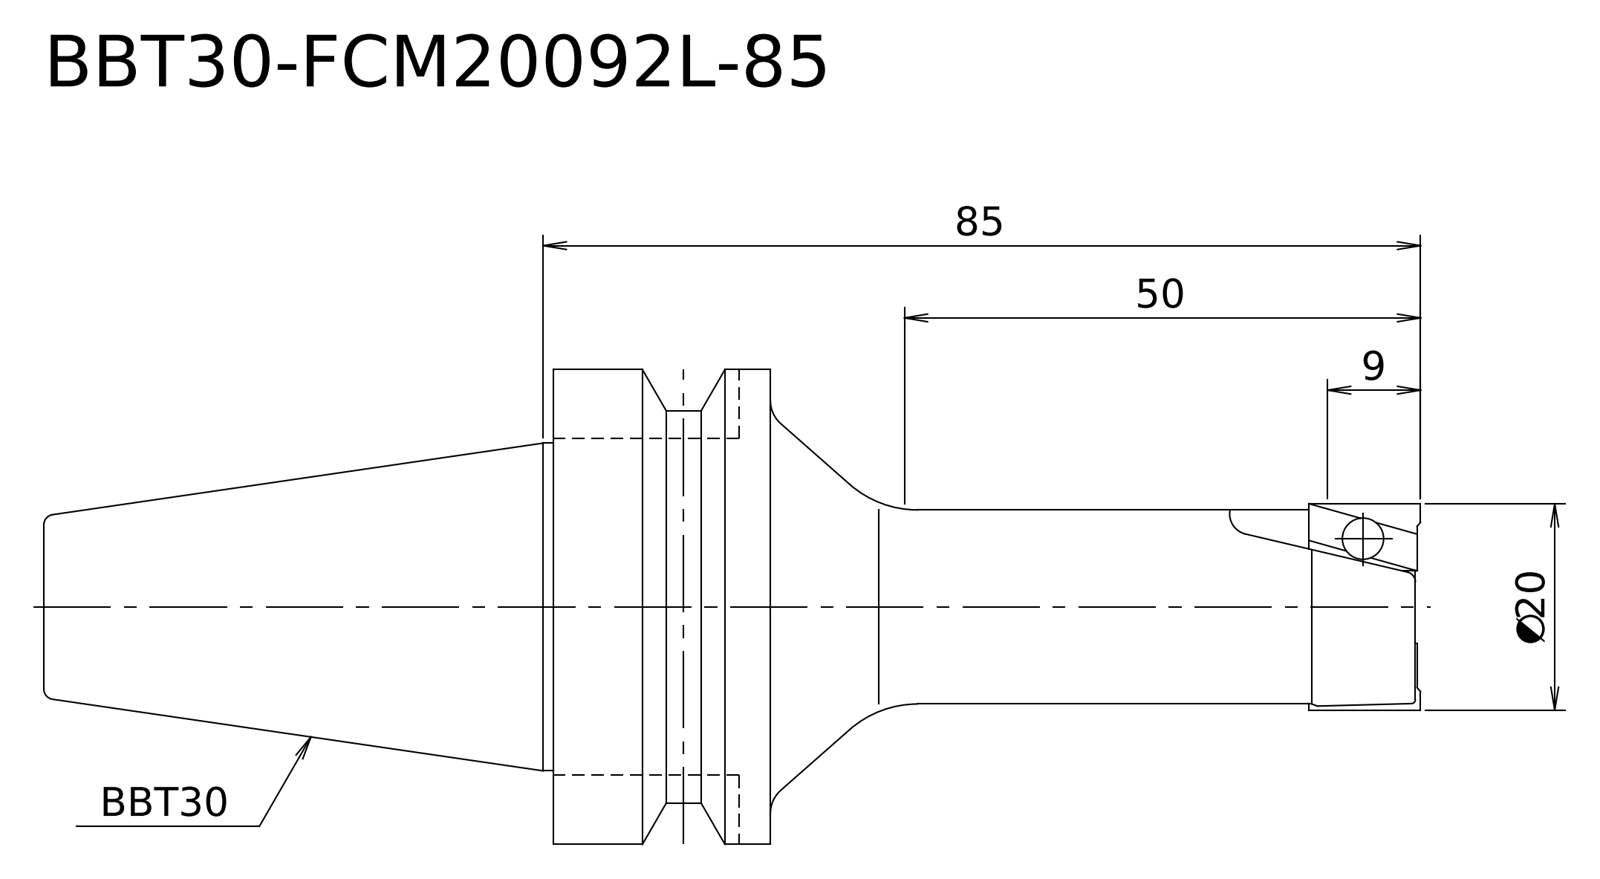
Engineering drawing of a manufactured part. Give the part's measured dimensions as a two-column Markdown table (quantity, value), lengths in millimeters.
| quantity | value |
| --- | --- |
| STEP written by | Kubotek KeyCreator V8.5.1 (14335) (CONFIG_CONTROL_DESIGN) |
| units | millimeters |
| bodies | 1 solid, 17 faces (4 planar, 6 cylindrical, 7 other) |
| overall size | 133.4 × 46 × 46 |
| volume | 78 492 mm³ |
| surface area | 13 741 mm² |
| round bosses / shafts (diameter × count) | 46 × 1, 38 × 1, 31.75 × 1, 20 × 1, 18.8 × 1 |
| main face-to-face distances | 21, 63, 84, 133.4, 70.4, 49.4 |
